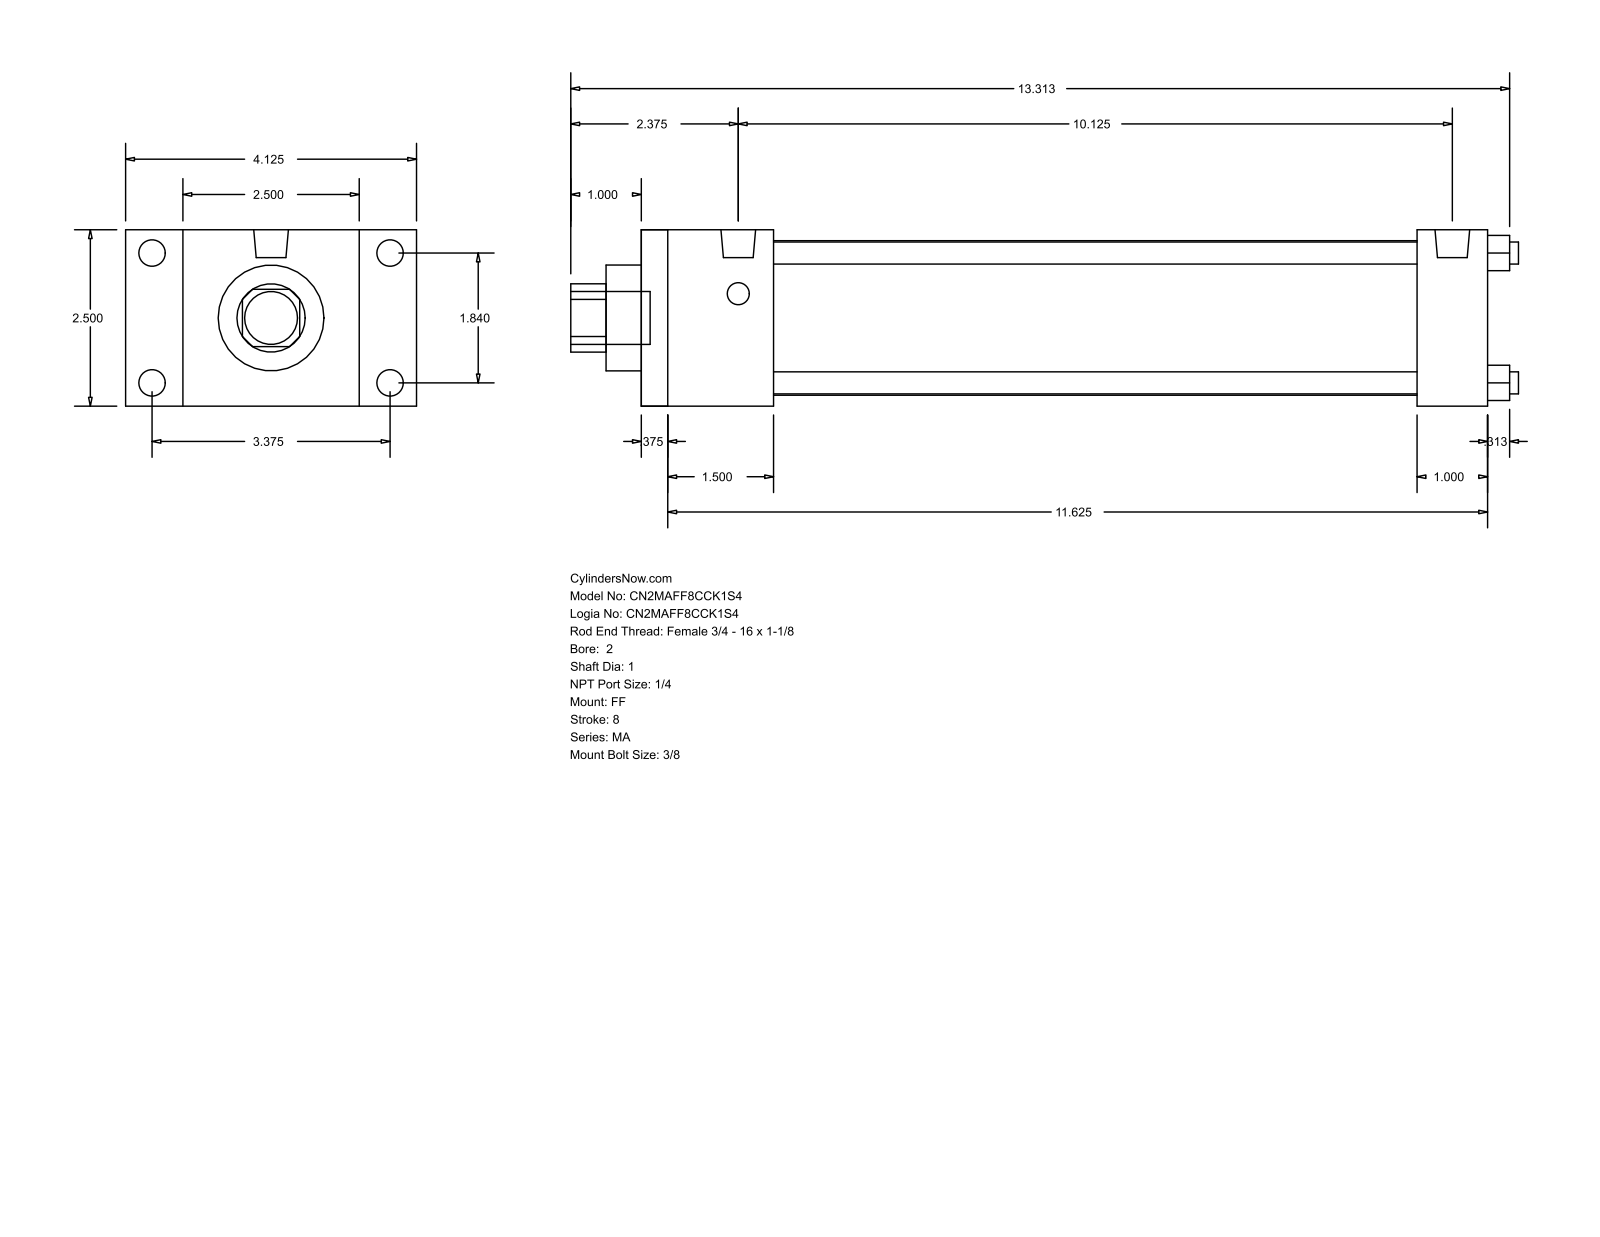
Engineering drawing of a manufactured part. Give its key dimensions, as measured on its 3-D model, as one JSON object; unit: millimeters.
{"part_name": "MA_FF__0200_1", "step_written_by": "GSSL Pune (CONFIG_CONTROL_DESIGN)", "units": "millimeters", "bodies": {"solids": 0, "faces": 92, "planar": 64, "cylindrical": 28, "other": 0}, "overall_size": [341.31, 104.78, 63.5], "round_holes": [[7.94, 4], [25.4, 1], [38.1, 1], [55.63, 1]], "round_bosses_or_shafts": [[9.53, 4], [7.94, 4], [12.49, 2], [19.05, 1]], "partial_cylinders_radius": [[12.29, 1]], "face_to_face_distances": [63.5, 304.8, 9.52, 295.28, 25.4, 20.64, 12.7, 47.63, 279.4, 38.11], "hole_center_spacings": [33.05, 46.74, 66.1]}
